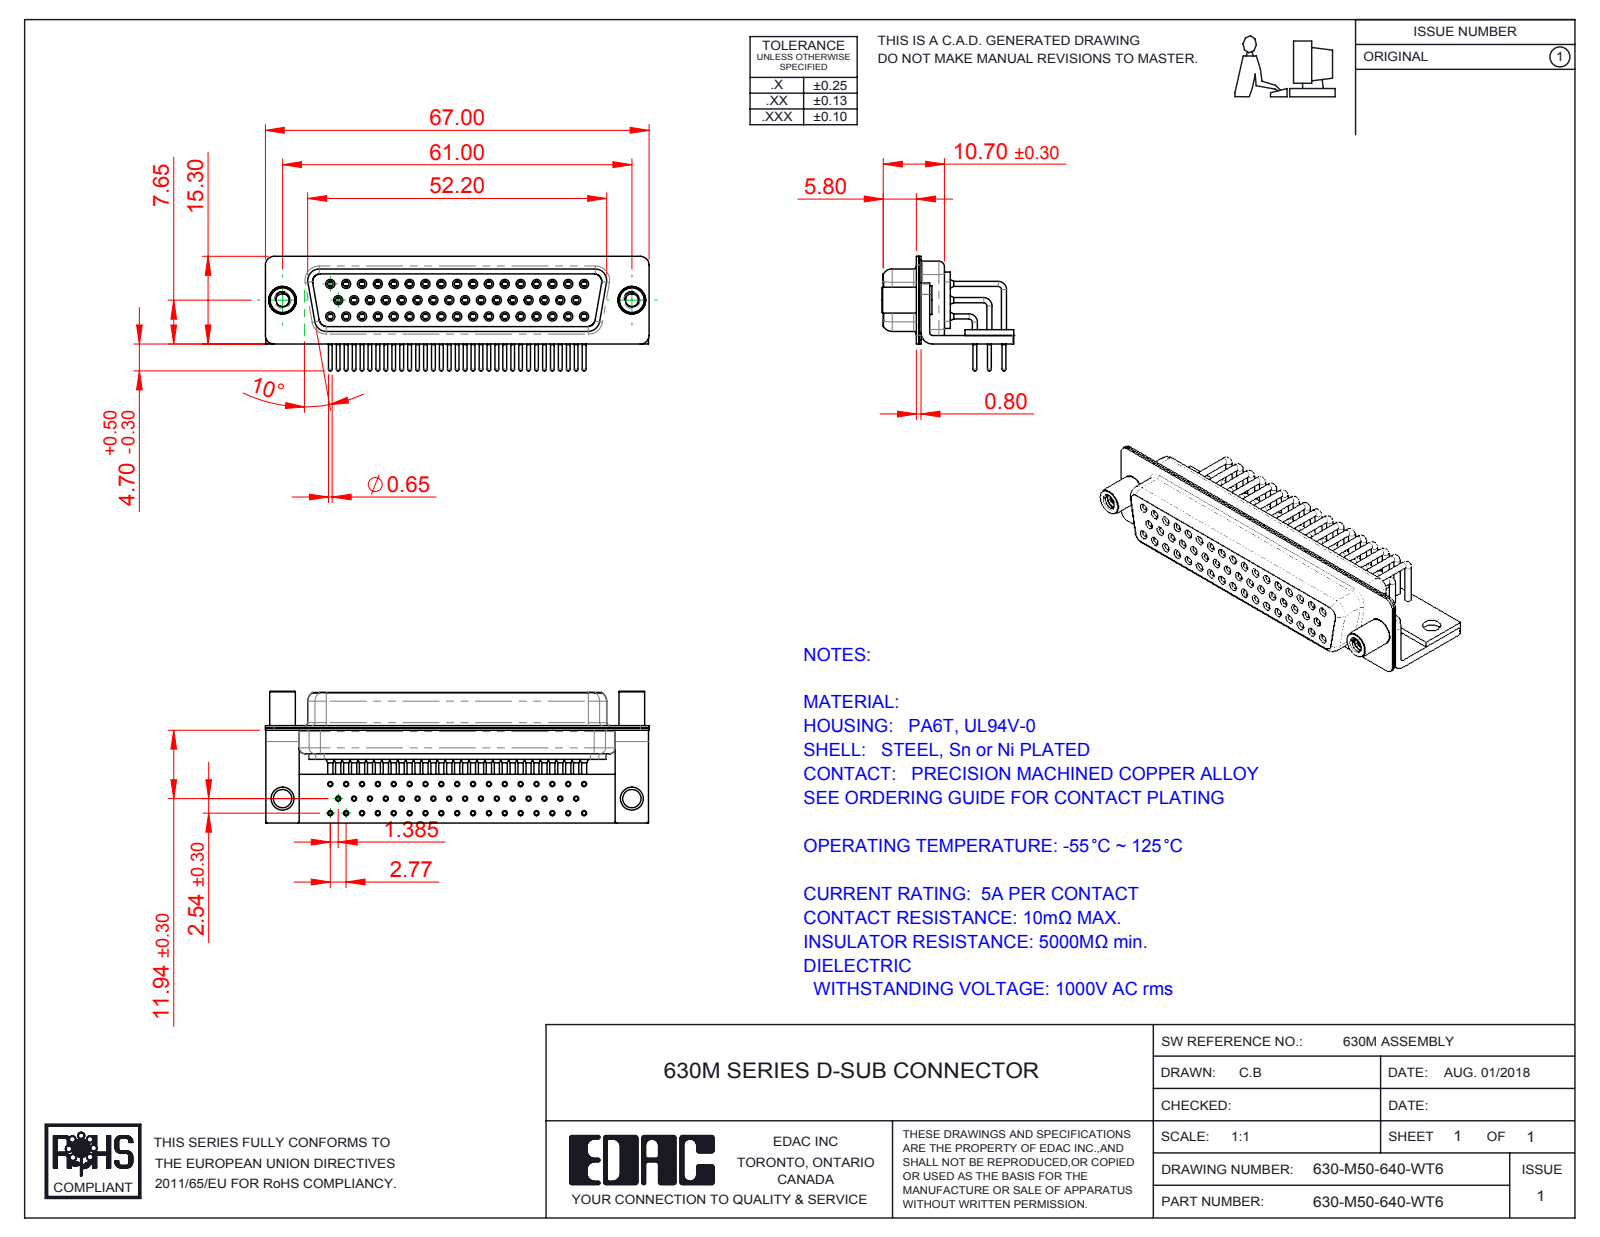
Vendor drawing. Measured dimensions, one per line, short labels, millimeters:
name: 630-M50-640-WT6; 630M Shell Front_50 Contacts; 630M Shell Rear_50 Contacts; 630M Stabilizer Bracket_50 Contacts (+6 more)
written by: SolidWorks 2016 (CONFIG_CONTROL_DESIGN)
unit: mm
bodies: 58 solids, 3129 faces (845 planar, 1451 cylindrical, 833 other)
size: 67 × 23 × 20
volume: 7 991 mm³; area: 18 922 mm²
holes: 50× ⌀0.9, 50× ⌀1, 50× ⌀1.1, 50× ⌀1.7, 50× ⌀1.8, 50× ⌀2, 2× ⌀2.26, 2× ⌀3.2, 2× ⌀4, 2× ⌀4.8
bosses: 59× ⌀0.9, 50× ⌀1.6, 50× ⌀1.5, 50× ⌀0.65, 2× ⌀5, 2× ⌀4.9, 2× ⌀4.5
rounds: 16× R0.25, 16× R1.5, 13× R2, 8× R1.35, 8× R1.6, 5× R0.5, 4× R0.6, 4× R0.65
face distances: 0.4, 1, 2.2, 0.85, 1.35, 11.85, 12.25, 5.8, 0.8, 5.9
hole spacings: 2.77, 5.54, 8.31, 11.08, 13.85, 16.62, 3.16, 19.39
